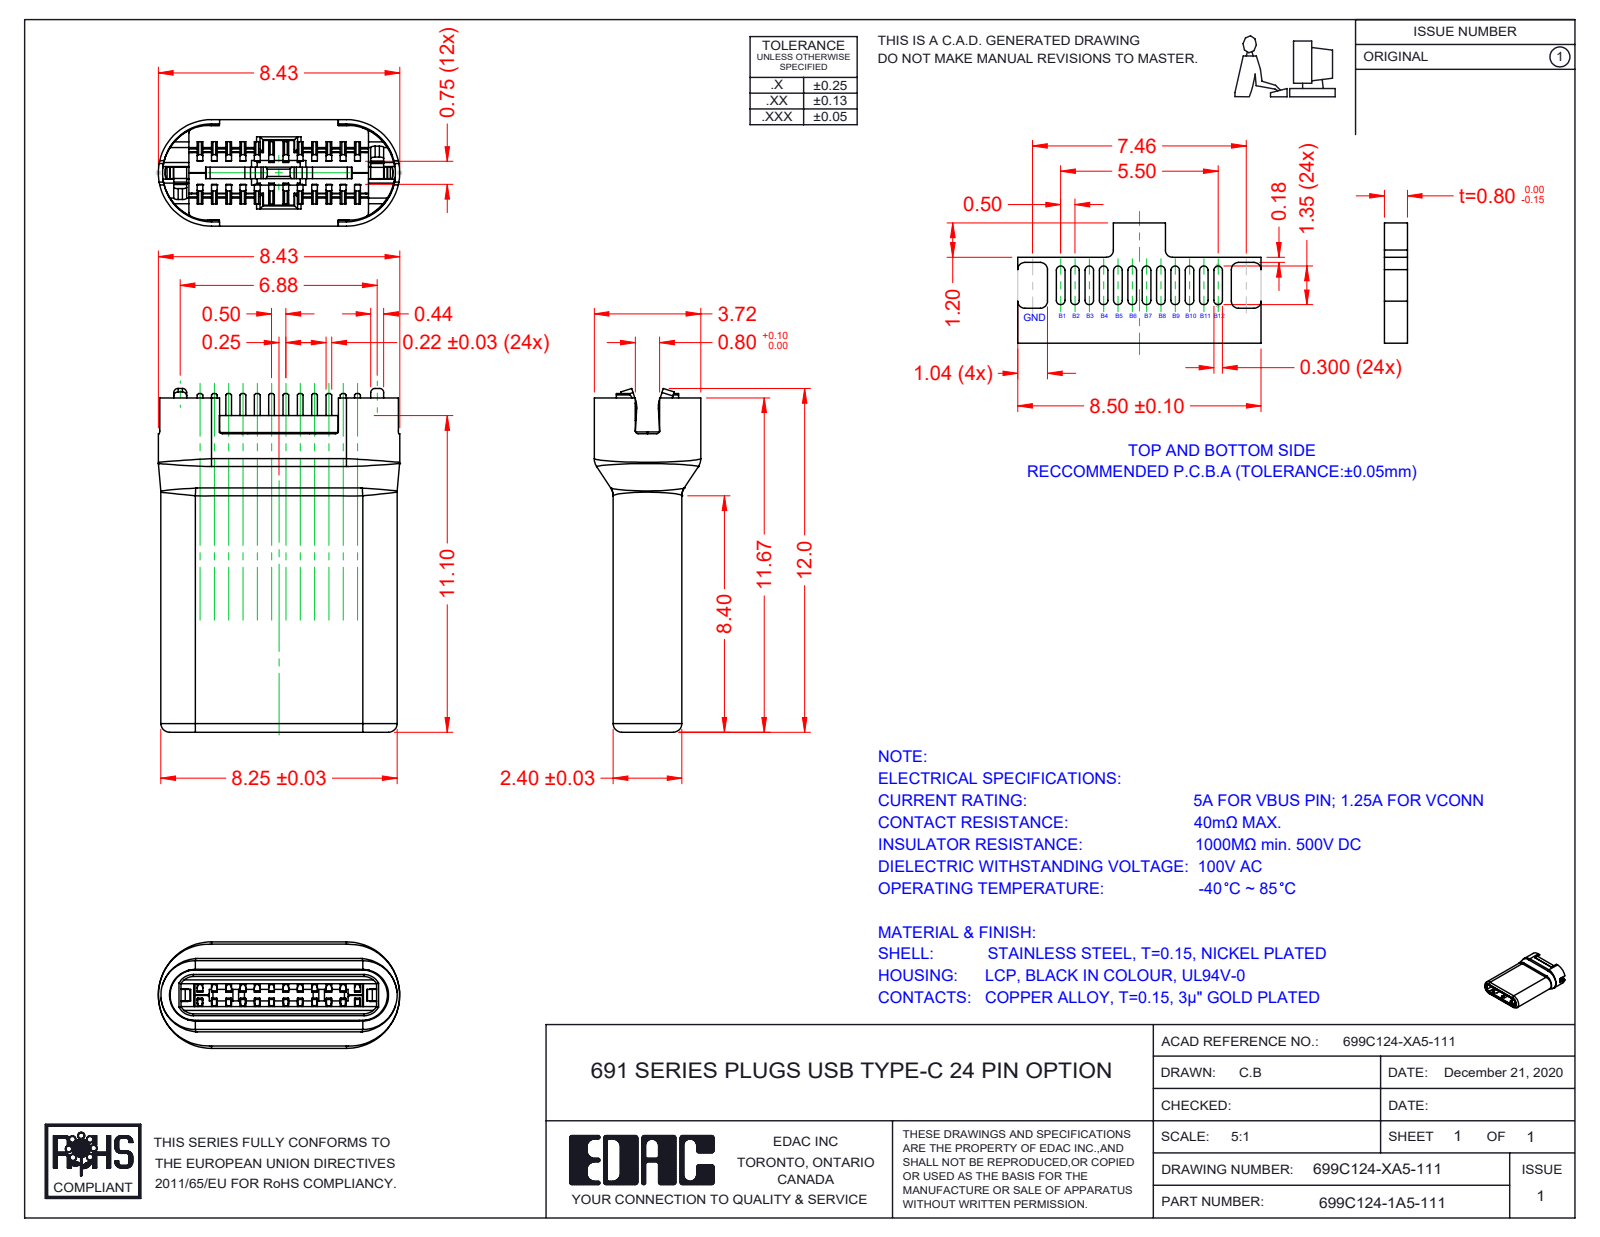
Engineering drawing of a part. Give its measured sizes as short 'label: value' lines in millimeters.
name: Ground 699C124-XA5-111; Shell 699C124-XA5-111; Insulator 699C124-XA5-111; Contacts 699C124-XA5-111 (+1 more)
written by: SolidWorks 2020 (AUTOMOTIVE_DESIGN)
unit: mm
bodies: 31 solids, 2291 faces (1650 planar, 551 cylindrical, 90 other)
size: 12 × 8.43 × 3.72
volume: 143 mm³; area: 1 465 mm²
rounds: 62× R0.15, 26× R0.2, 18× R0.13, 16× R0.1, 10× R0.3, 9× R0.12, 8× R0.5, 8× R1
face distances: 1, 0.5, 1.5, 0.85, 2, 2.25, 3, 3.5, 2.5, 1.25
